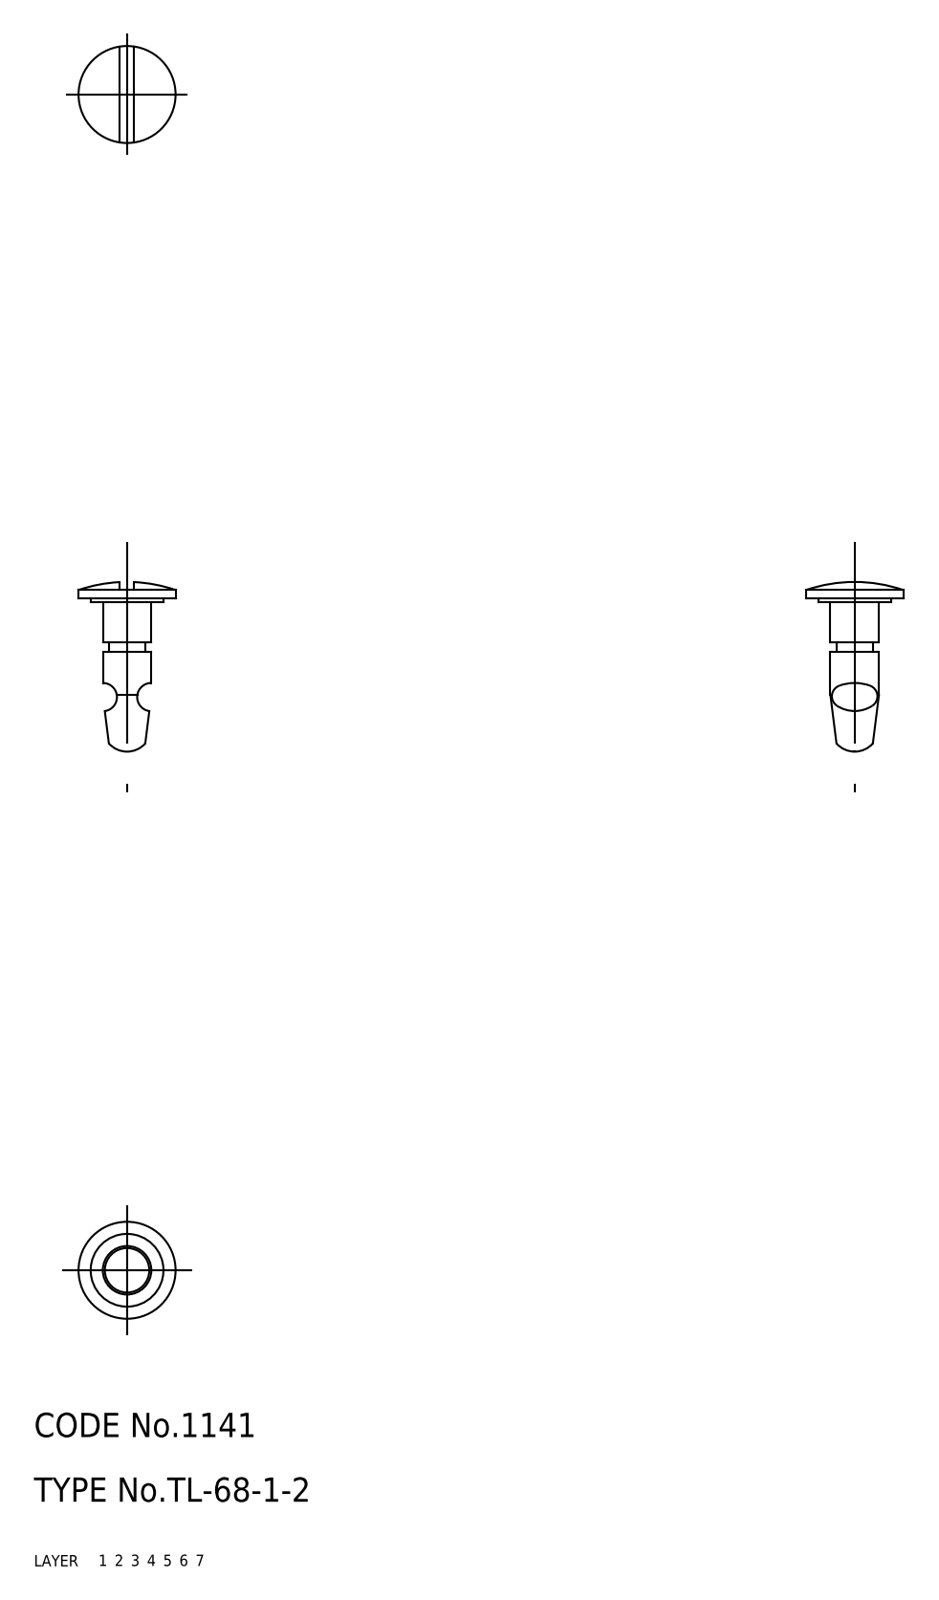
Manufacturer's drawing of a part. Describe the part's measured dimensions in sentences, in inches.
The part is named "fastener". Its 3-D file was written by "CADfix (AUTOMOTIVE_DESIGN)". It is 1 solid with 26 faces: 0 planar, 0 cylindrical and 26 other. Overall it measures 0.826 by 0.472 by 0.472 inches. Its volume is 0.037 cubic inches and its surface area 0.973 square inches.
